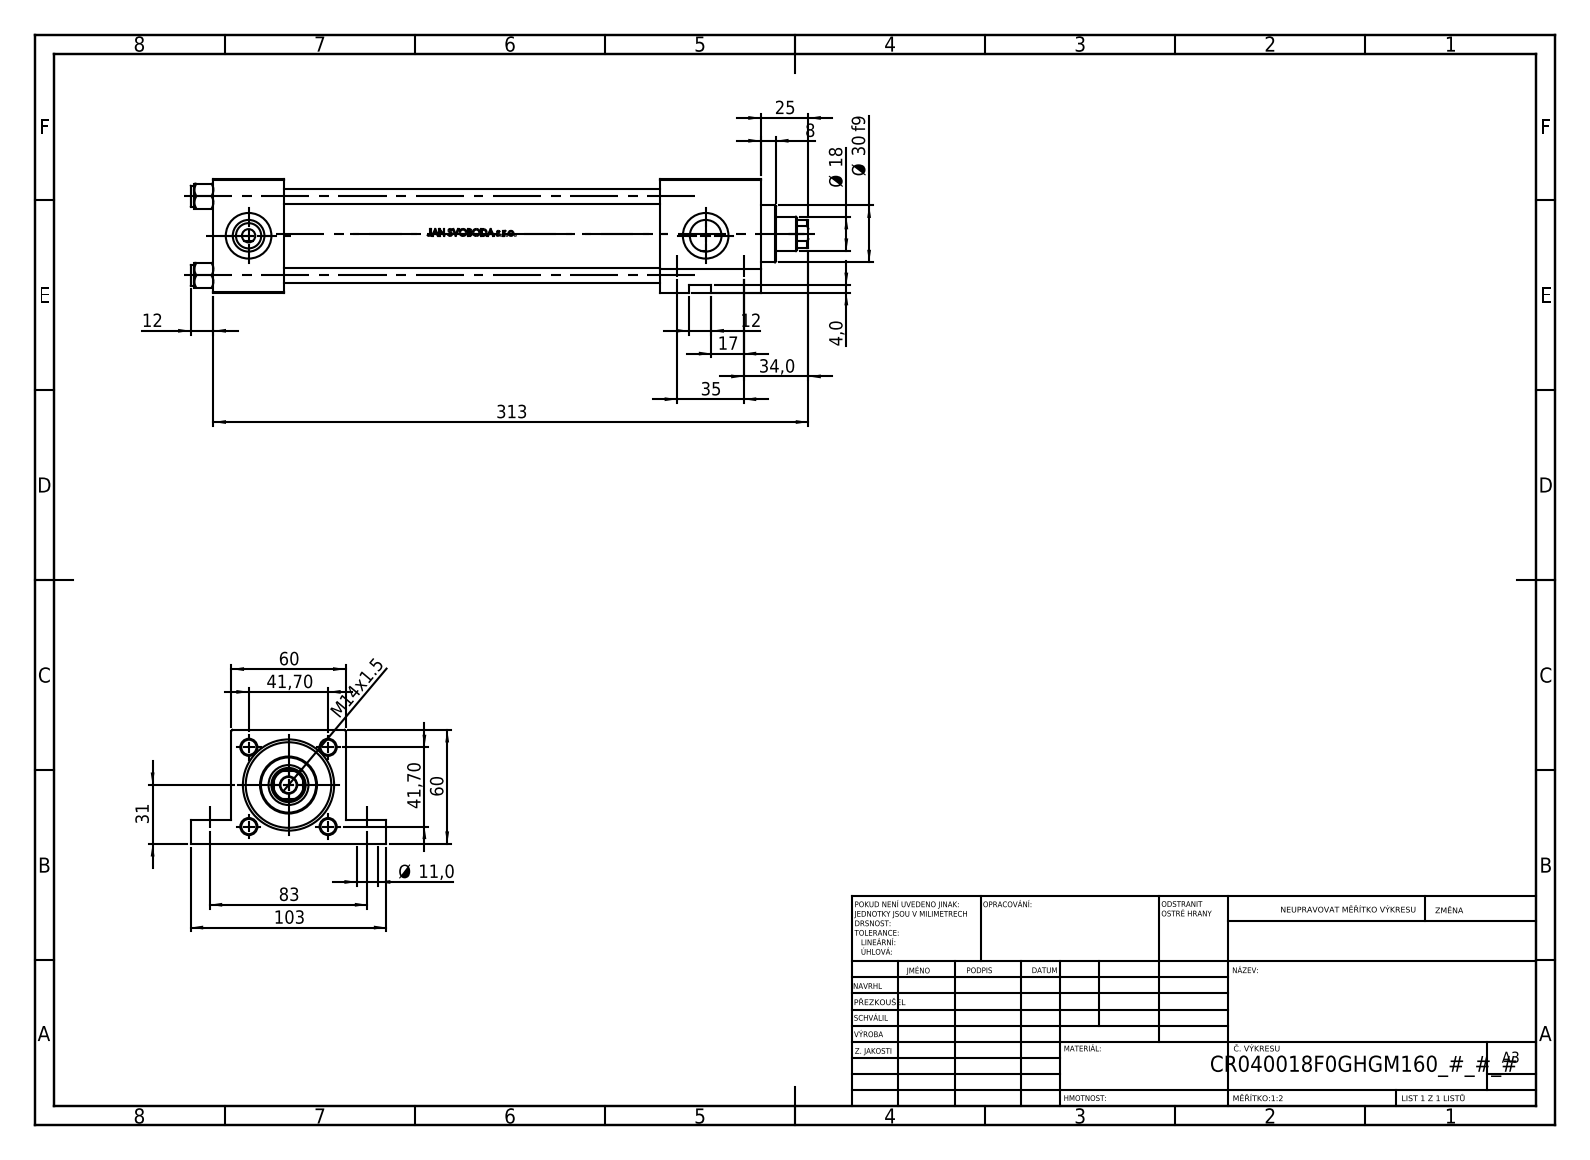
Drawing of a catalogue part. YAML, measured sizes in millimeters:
part_name: "V215_VC_A; V215CR_F_Body; V215CR_VCP_F; NUT_M5_F (+1 more)"
step_written_by: "SolidWorks 2019 (CONFIG_CONTROL_DESIGN)"
units: millimeters
bodies: {solids: 11, faces: 1118, planar: 437, cylindrical: 141, other: 540}
overall_size: [325, 103, 60]
volume: 544143
surface_area: 171353
round_holes:
  - {diameter: 8, count: 4}
  - {diameter: 11, count: 4}
  - {diameter: 7, count: 2}
  - {diameter: 16.66, count: 2}
  - {diameter: 24, count: 2}
  - {diameter: 8.5, count: 1}
  - {diameter: 18, count: 1}
  - {diameter: 21, count: 1}
  - {diameter: 31, count: 1}
  - {diameter: 40, count: 1}
  - {diameter: 45, count: 1}
round_bosses_or_shafts:
  - {diameter: 11, count: 4}
  - {diameter: 46, count: 1}
  - {diameter: 30, count: 1}
partial_cylinders:
  - {radius: 8.5, count: 1}
face_to_face_distances: [60, 37, 288, 251, 235, 198, 53, 259.3, 222.3, 24.3]
hole_center_spacings: [41.7, 28.79, 30.2, 35, 58.97, 83, 90.08, 240.5]
